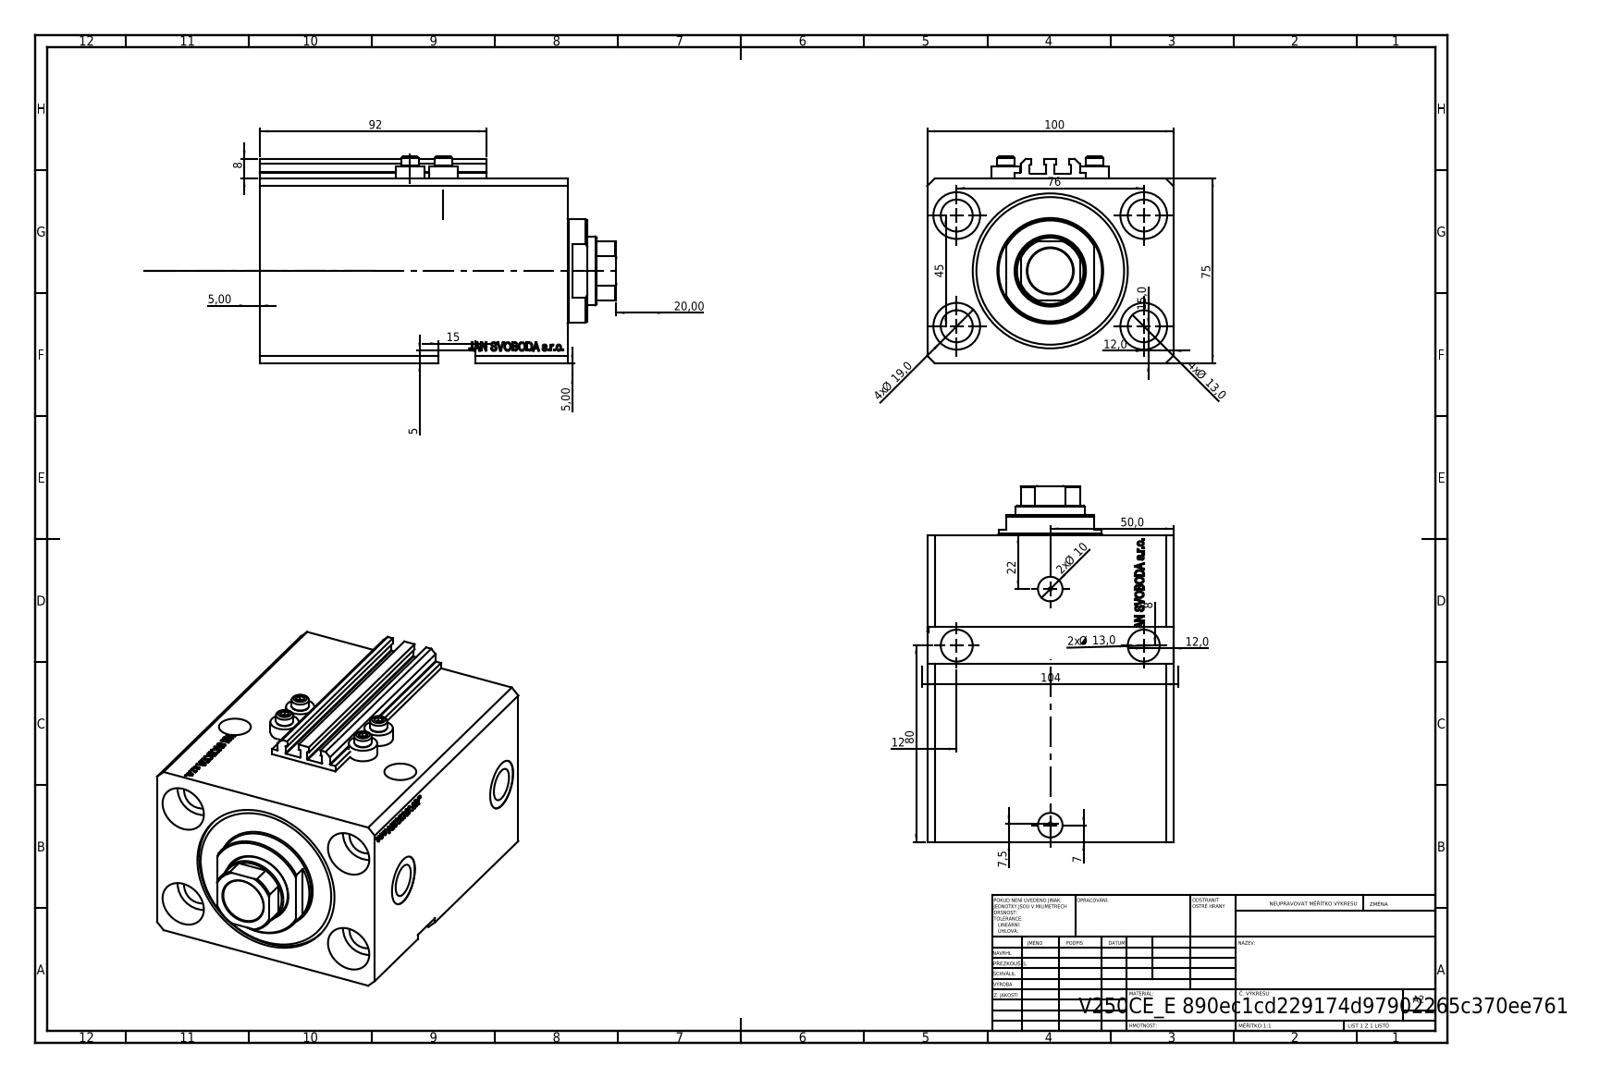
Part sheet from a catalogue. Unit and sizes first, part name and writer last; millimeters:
Units: millimetres
Overall size (bounding box): 144.9 × 100 × 84
Round holes (diameter × count): ⌀13 ×6, ⌀1.25 ×4, ⌀4 ×4, ⌀19 ×4, ⌀10 ×2, ⌀13.16 ×2, ⌀20 ×2, ⌀18.5 ×1, ⌀28 ×1, ⌀50 ×1, ⌀63 ×1
Round bosses / shafts (diameter × count): ⌀11.6 ×4, ⌀7 ×4, ⌀42 ×1
Partial cylindrical surfaces — rounded edges, fillets, slot ends (radius × count): R0.2 ×10, R13.5 ×1
Main face-to-face distances: 75, 100, 125, 11.9, 113.1, 98.4, 86.5, 26.6, 48.4, 5
Hole centre spacings: 44.16, 76, 13.6, 20.72, 27.59, 33.62, 36, 38.48
Volume: 782 818 mm³ · Surface area: 149 099 mm²
Bodies: 8 solids, 1088 faces (535 planar, 126 cylindrical, 427 other)
Part name (STEP PRODUCT): V250CE_E_Body; ALLEN BOLT V250CE; V250CE_VC_E; V250CE_C_VCP
STEP written by: SolidWorks 2019 (CONFIG_CONTROL_DESIGN)
